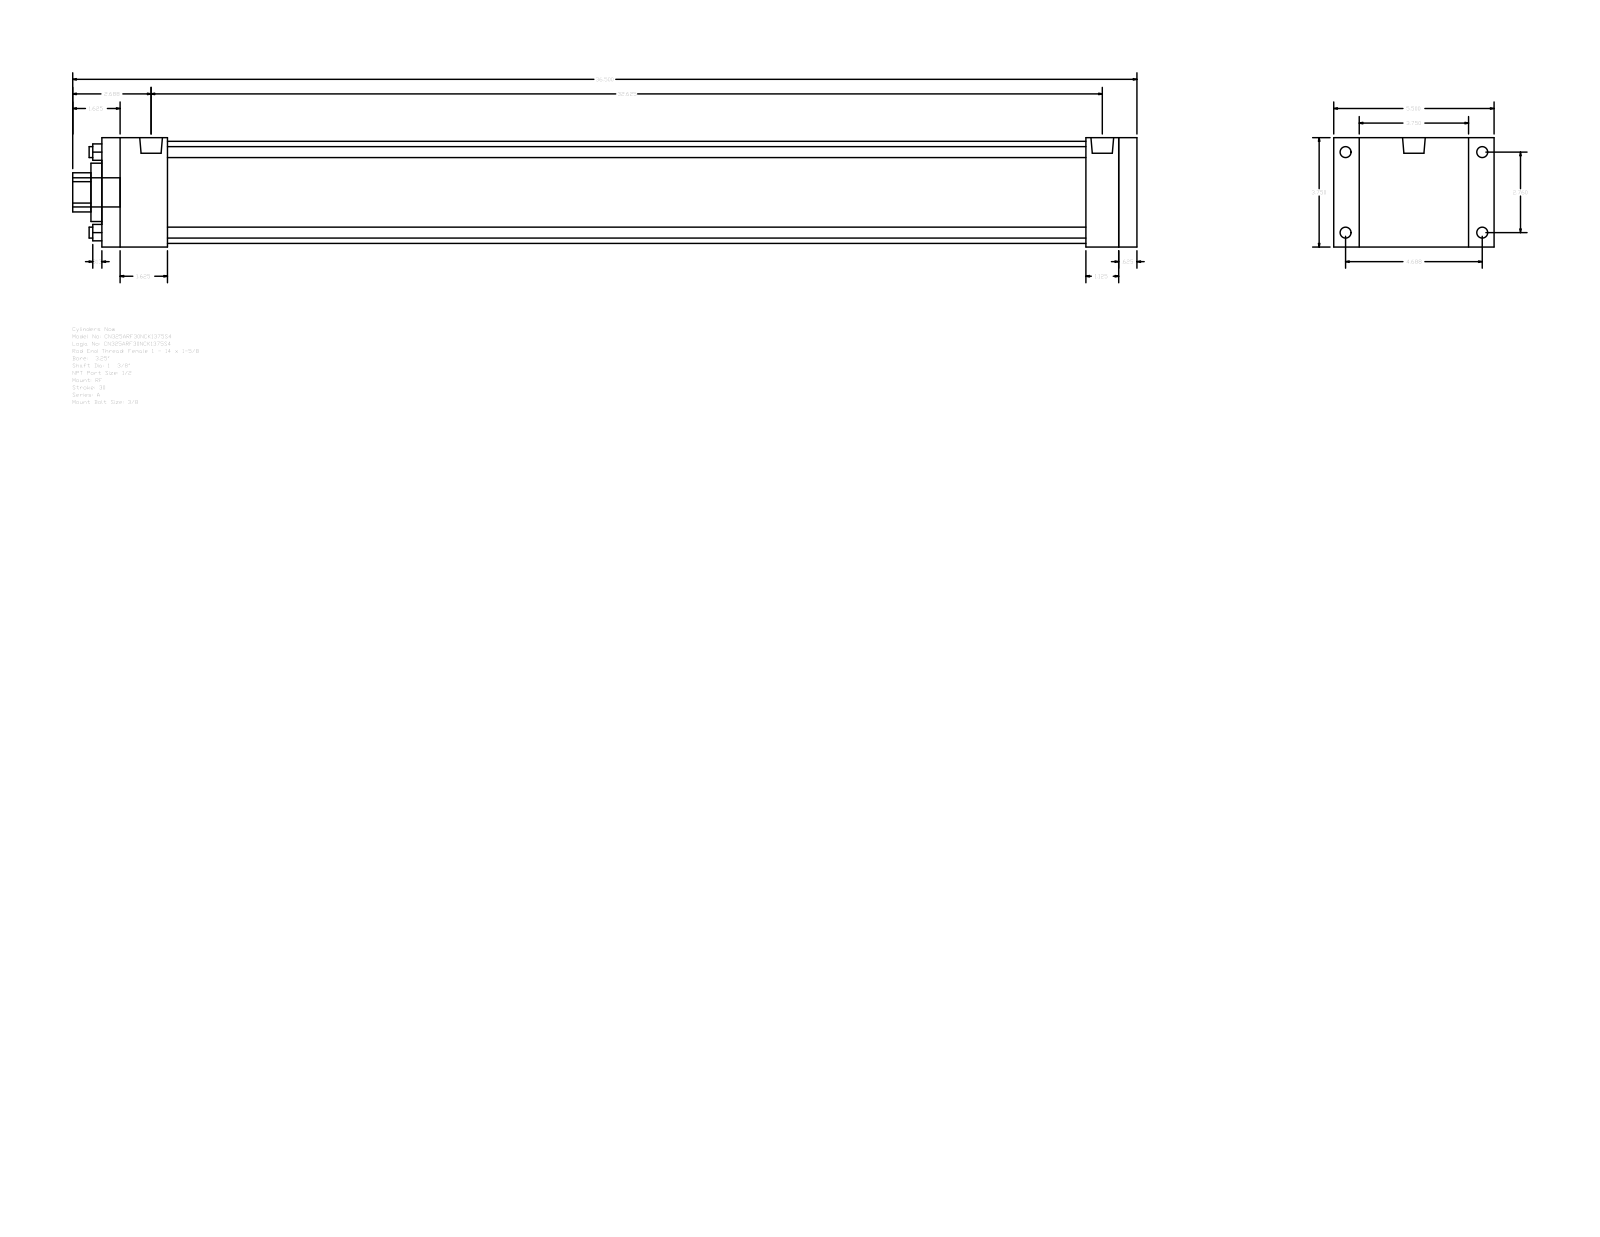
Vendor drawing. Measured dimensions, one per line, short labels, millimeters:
name: A_RF__0325_1.375
written by: GSSL Pune (CONFIG_CONTROL_DESIGN)
unit: mm
bodies: 0 solids, 92 faces (64 planar, 28 cylindrical, 0 other)
size: 927.1 × 139.7 × 95.25
holes: 4× ⌀9.53, 1× ⌀34.92, 1× ⌀50.8, 1× ⌀88.9
bosses: 4× ⌀9.53, 4× ⌀8.73, 2× ⌀19.77, 1× ⌀25.4
rounds: 1× R17.06
face distances: 95.24, 901.7, 15.87, 885.83, 28.58, 22.23, 117.47, 857.25, 44.45, 57.15
hole spacings: 49.57, 70.1, 99.14
